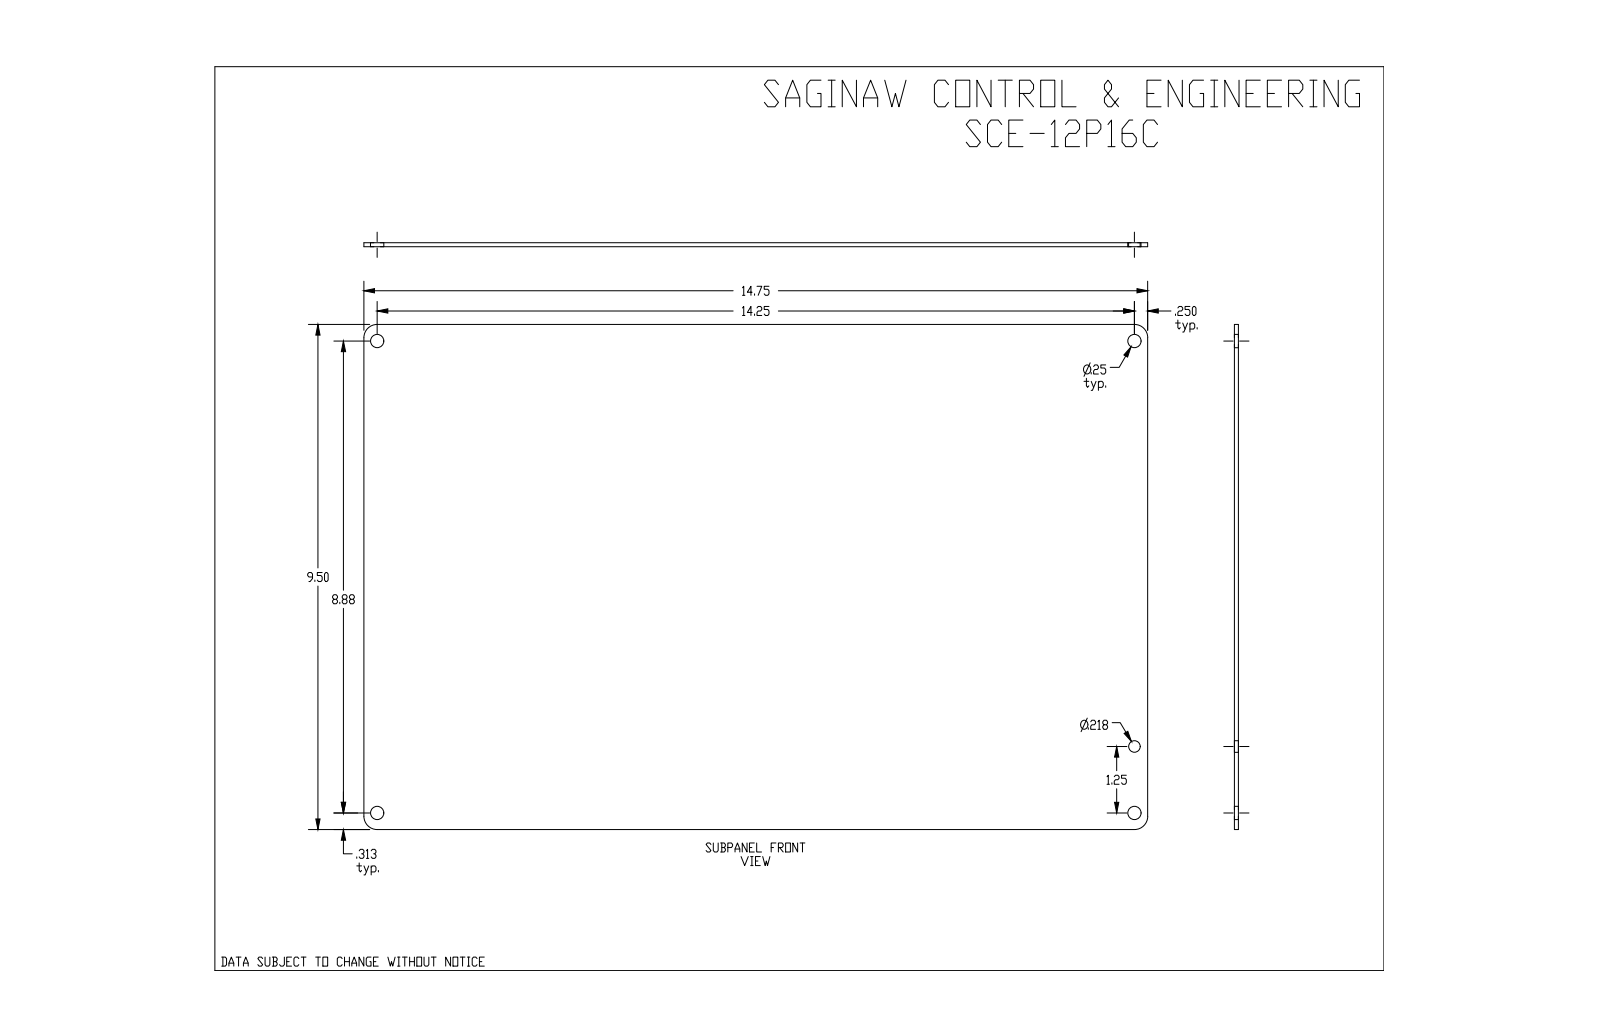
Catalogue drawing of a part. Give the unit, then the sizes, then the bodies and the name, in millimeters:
Units: millimetres
Overall size (bounding box): 374.7 × 241.3 × 1.9
Round holes (diameter × count): ⌀6.4 ×4, ⌀5.5 ×1
Partial cylindrical surfaces — rounded edges, fillets, slot ends (radius × count): R6.4 ×4
Main face-to-face distances: 1.9, 241.3, 374.7
Hole centre spacings: 225.4, 362, 426.4, 31.8, 193.7, 363.3, 410.5
Volume: 171 900 mm³ · Surface area: 183 000 mm²
Bodies: 1 solid, 15 faces (6 planar, 9 cylindrical, 0 other)
Part name (STEP PRODUCT): SCE-12P16C
STEP written by: SolidWorks 2019 (CONFIG_CONTROL_DESIGN)
